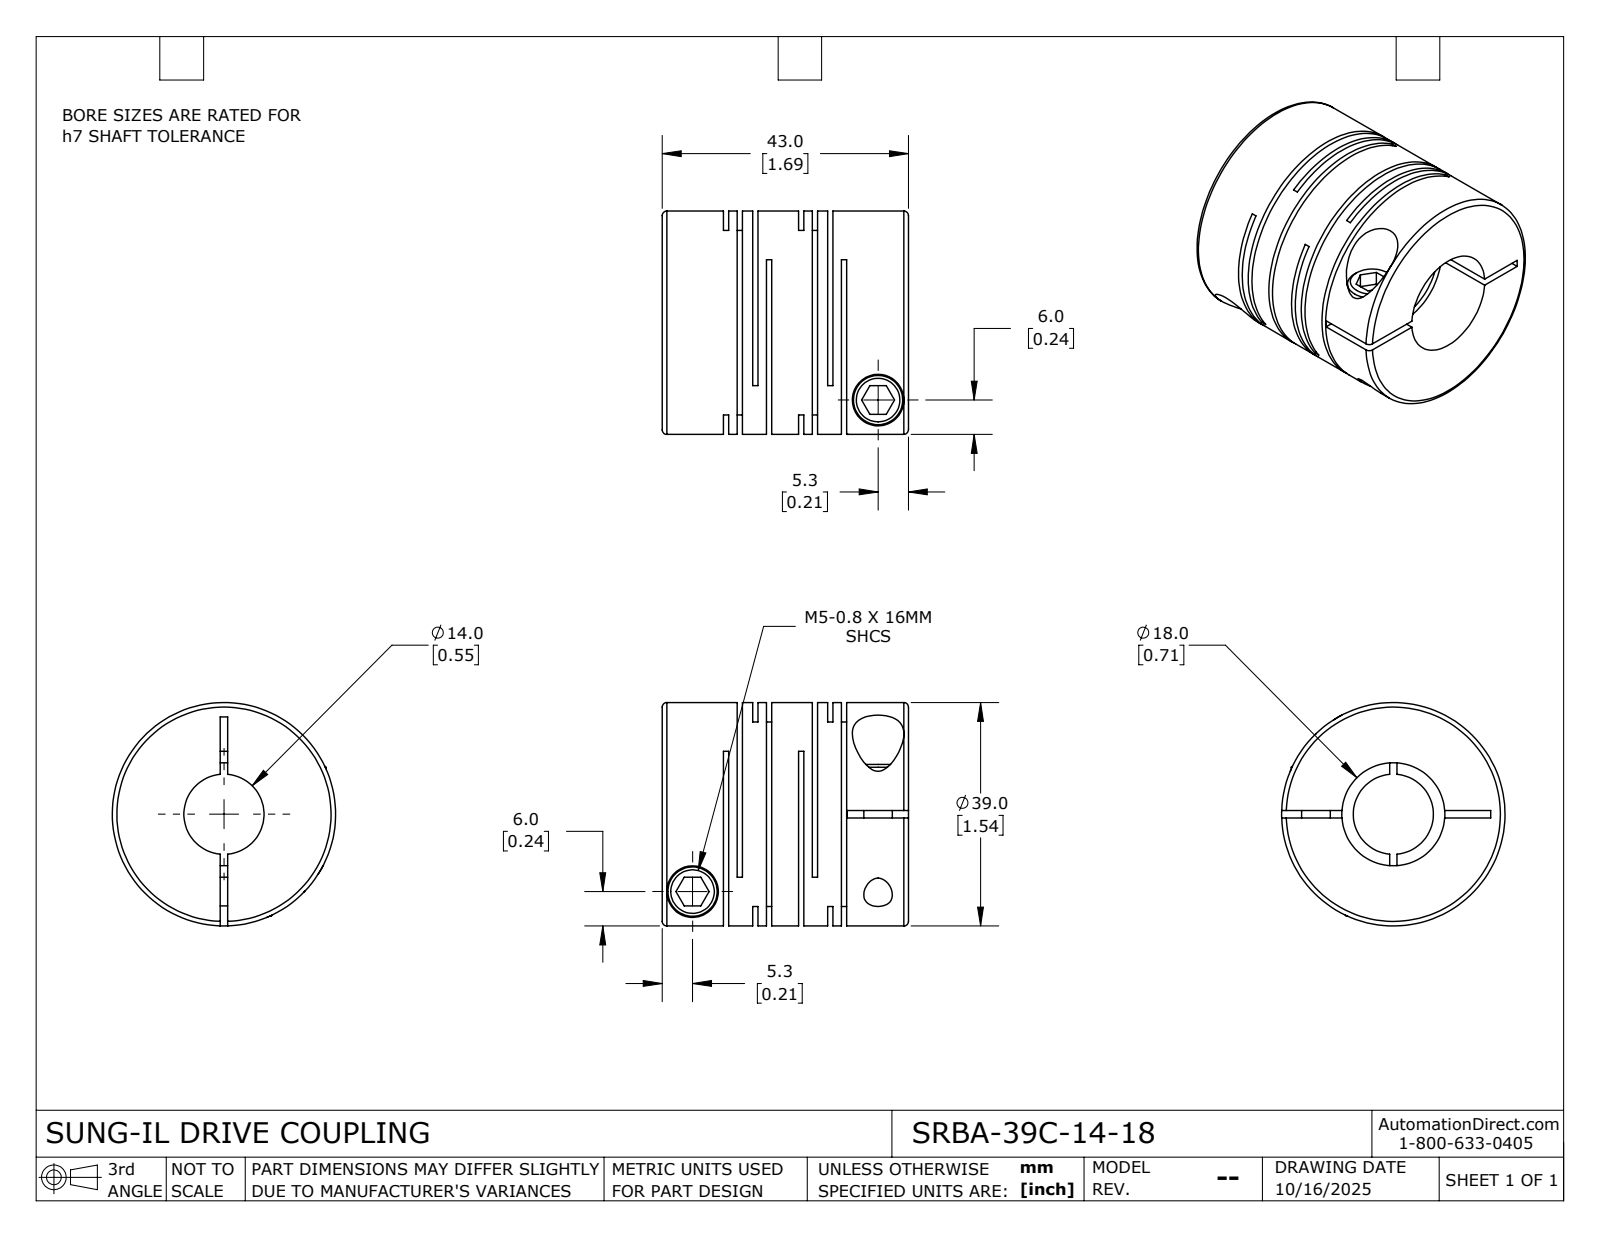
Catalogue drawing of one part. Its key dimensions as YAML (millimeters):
part_name: "SRBA-39C-14-18"
step_written_by: "SolidWorks 2024 (CONFIG_CONTROL_DESIGN)"
units: millimeters
bodies: {solids: 1, faces: 115, planar: 60, cylindrical: 42, other: 13}
overall_size: [43, 39, 39]
volume: 34535
surface_area: 22271
round_holes:
  - {diameter: 5, count: 2}
  - {diameter: 9, count: 2}
  - {diameter: 14, count: 1}
  - {diameter: 18, count: 1}
round_bosses_or_shafts:
  - {diameter: 8.6, count: 2}
  - {diameter: 39, count: 1}
face_to_face_distances: [13.1, 0.92, 2.4, 5.1, 10.7, 14.02, 18.2, 7.5, 12.18, 3.32]
